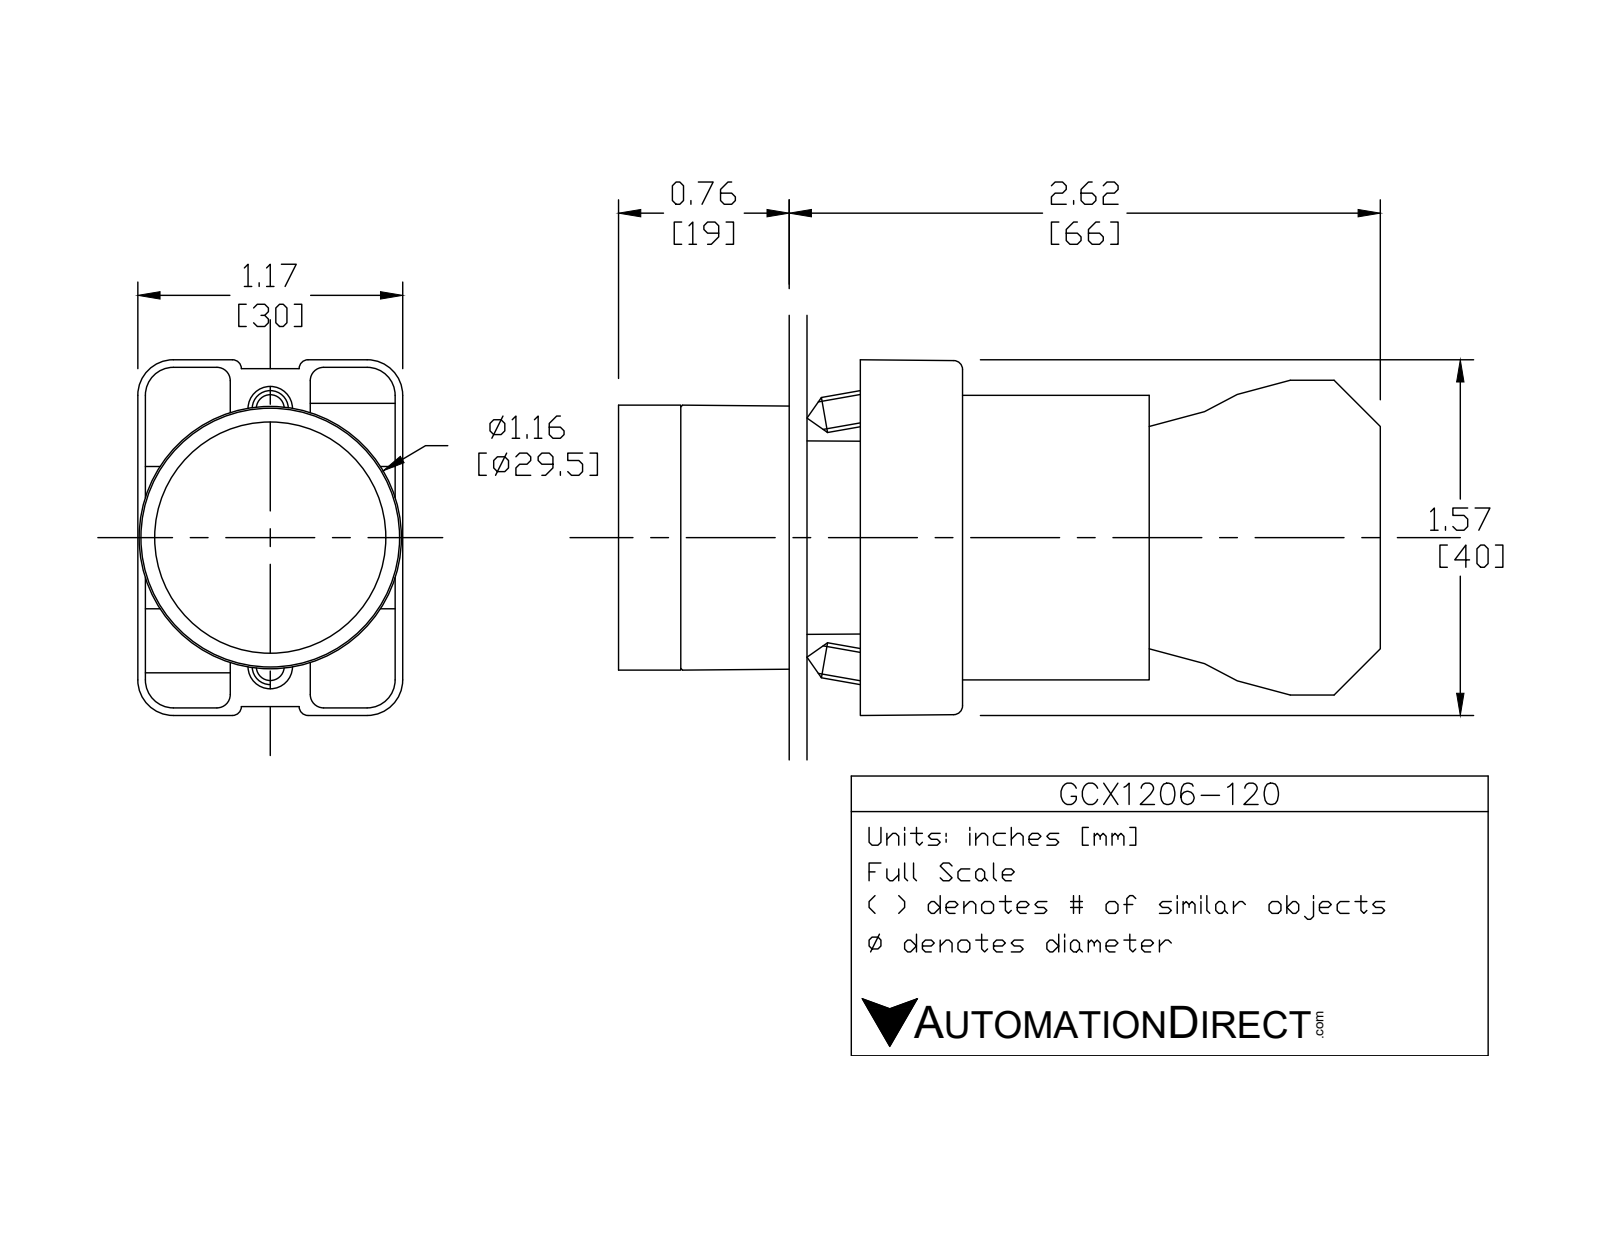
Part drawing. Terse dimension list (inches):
name: ecx1029; GCX1206-120; GCX1206 OPERATOR; ECX1050 (+1 more)
written by: SolidWorks 2016 (AUTOMOTIVE_DESIGN)
unit: in
bodies: 8 solids, 431 faces (252 planar, 148 cylindrical, 31 other)
size: 3.319 × 1.581 × 1.177
volume: 2.794 in³; area: 38.75 in²
holes: 2× ⌀0.079, 2× ⌀0.124, 2× ⌀0.13, 1× ⌀0.087, 1× ⌀0.197, 1× ⌀0.469, 1× ⌀0.878, 1× ⌀0.888, 1× ⌀1.024
bosses: 4× ⌀0.157, 1× ⌀1.175, 1× ⌀1.004, 1× ⌀0.945, 1× ⌀0.856, 1× ⌀0.78, 1× ⌀0.504
rounds: 24× R0.059, 12× R0.041, 12× R0.124, 12× R0.157, 8× R0.039, 2× R0.128, 1× R0.02, 1× R0.063
face distances: 0.827, 2.02, 1.193, 0.579, 1.171, 0.031, 0.276, 0.033, 0.748, 0.573
hole spacings: 0.236, 0.544, 0.472, 0.49
